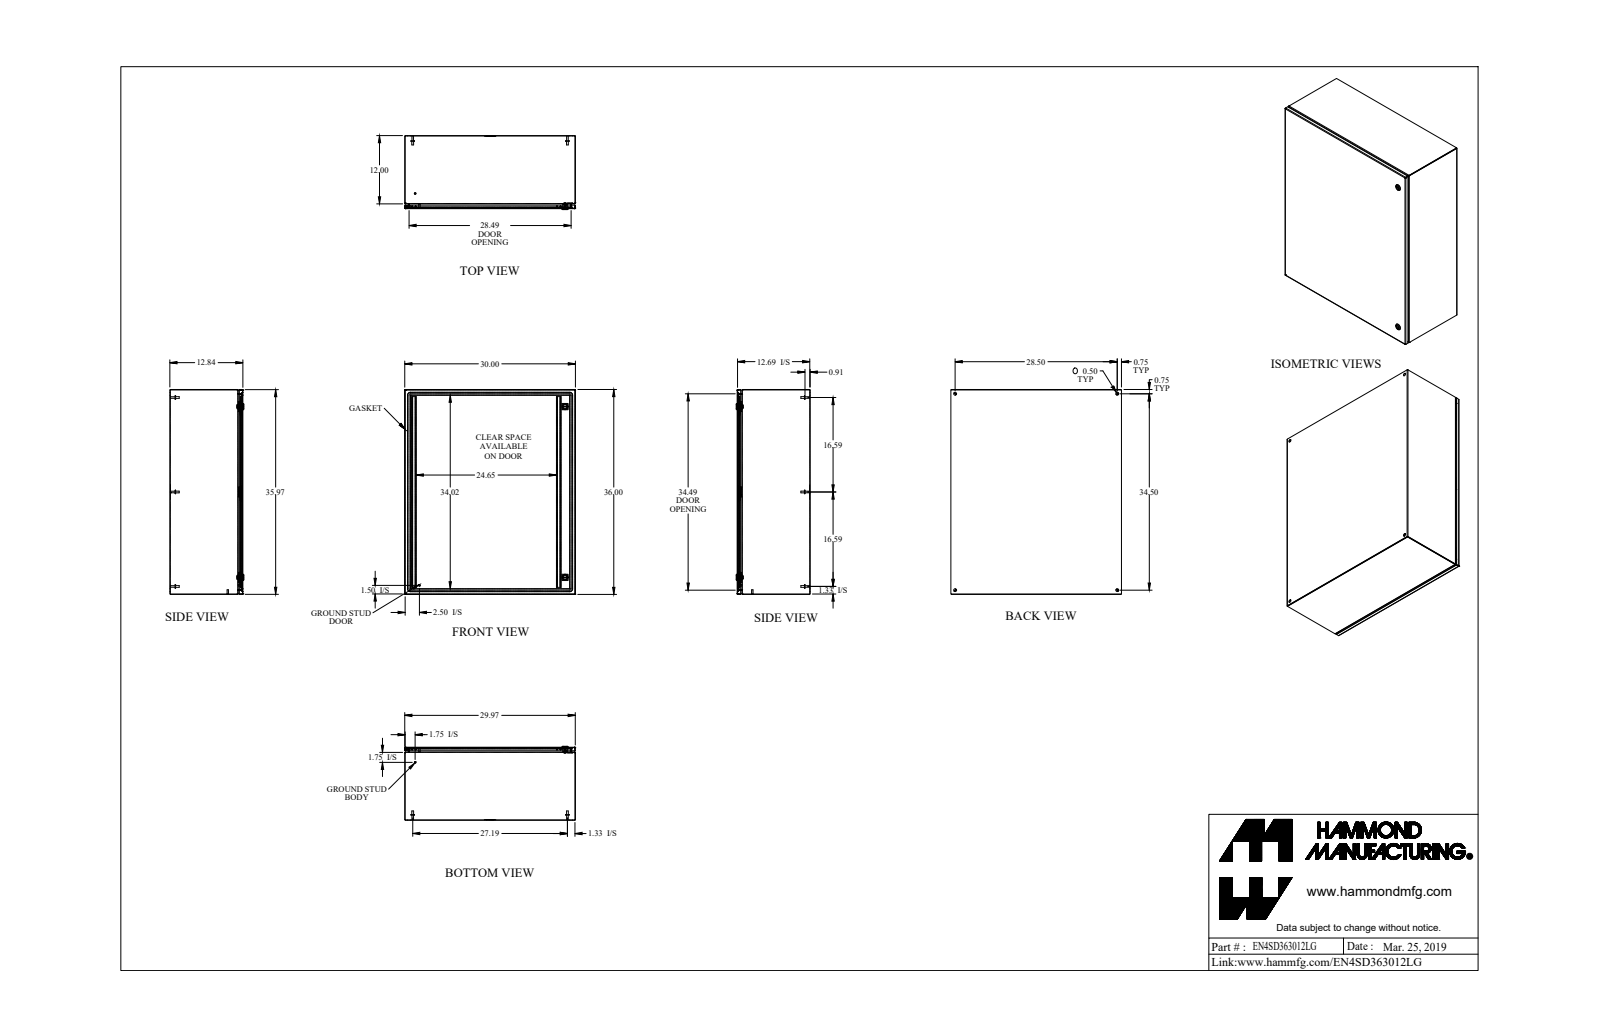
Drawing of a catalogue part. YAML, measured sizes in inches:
part_name: "EN4SD363012LG"
step_written_by: "SolidWorks 2019 (AUTOMOTIVE_DESIGN)"
units: inches
bodies: {solids: 35, faces: 901, planar: 434, cylindrical: 295, other: 172}
overall_size: [36, 30, 12.997]
volume: 305.3
surface_area: 8558
round_holes:
  - {diameter: 0.5, count: 4}
  - {diameter: 0.232, count: 2}
  - {diameter: 0.625, count: 2}
  - {diameter: 0.785, count: 2}
  - {diameter: 0.172, count: 1}
  - {diameter: 0.24, count: 1}
  - {diameter: 0.242, count: 1}
round_bosses_or_shafts:
  - {diameter: 0.625, count: 6}
  - {diameter: 0.313, count: 6}
  - {diameter: 0.27, count: 6}
  - {diameter: 1.1, count: 2}
  - {diameter: 0.525, count: 2}
  - {diameter: 0.281, count: 2}
  - {diameter: 0.25, count: 2}
  - {diameter: 0.455, count: 1}
partial_cylinders:
  - {radius: 0.036, count: 18}
  - {radius: 0.108, count: 18}
  - {radius: 0.043, count: 12}
  - {radius: 0.081, count: 12}
  - {radius: 0.312, count: 12}
  - {radius: 0.006, count: 6}
  - {radius: 0.062, count: 6}
  - {radius: 0.125, count: 4}
face_to_face_distances: [0.072, 12.765, 12.693, 12.837, 29.928, 35.928, 29.856, 30, 35.856, 36]
hole_center_spacings: [27.519, 28.5, 34.5, 44.749, 2.493, 2.494, 29.999, 32.267]
